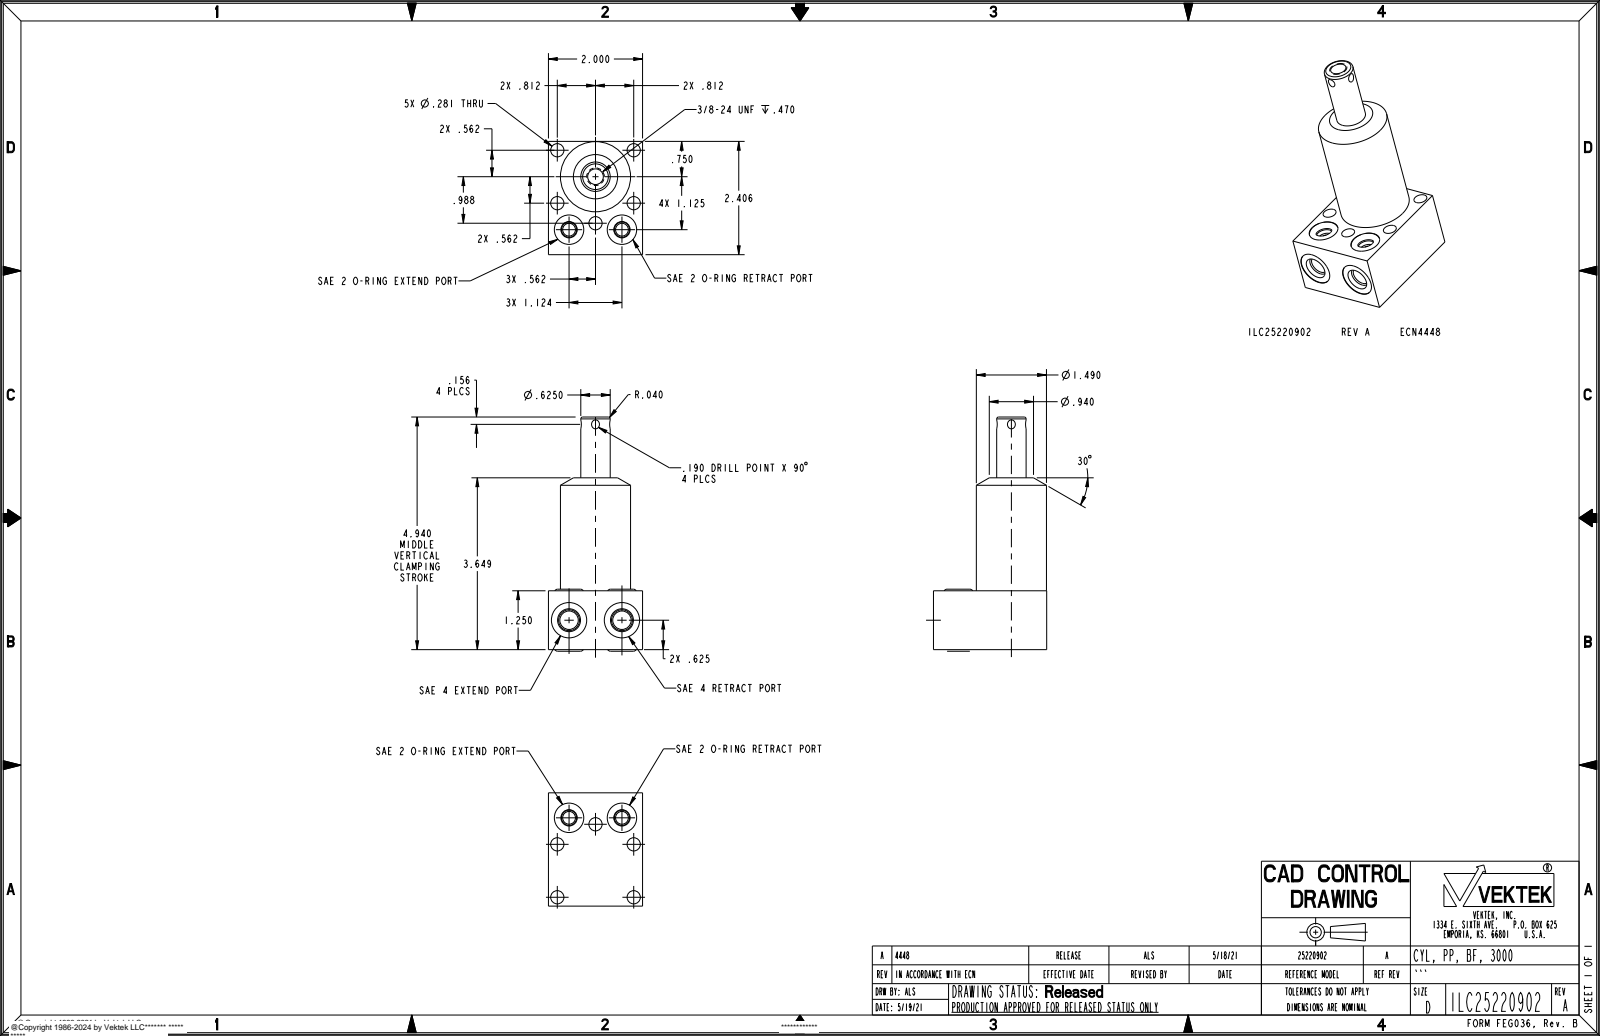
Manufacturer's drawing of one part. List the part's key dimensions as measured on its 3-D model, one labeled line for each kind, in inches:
Part name (STEP PRODUCT): ILC25220902
STEP written by: PRO/ENGINEER BY PARAMETRIC TECHNOLOGY CORPORATION, 2013320 (CONFIG_CONTROL_DESIGN)
Units: inches
Bodies: 5 solids, 113 faces (17 planar, 42 cylindrical, 54 other)
Overall size (bounding box): 4.974 × 2.406 × 2
Volume: 9.731 in³ · Surface area: 45.96 in²
Round holes (diameter × count): ⌀0.281 ×5, ⌀0.272 ×2, ⌀0.392 ×2, ⌀0.625 ×2, ⌀0.75 ×2, ⌀0.332 ×1
Round bosses / shafts (diameter × count): ⌀1.49 ×1, ⌀0.625 ×1, ⌀0.375 ×1
Main face-to-face distances: 2, 1.25, 2.406, 0.105, 1.145, 2.396, 1.04, 3.649, 3.544, 2.504
Hole centre spacings: 0.987, 1.124, 0.578, 0.616, 0.917, 1.257, 1.485, 1.624
